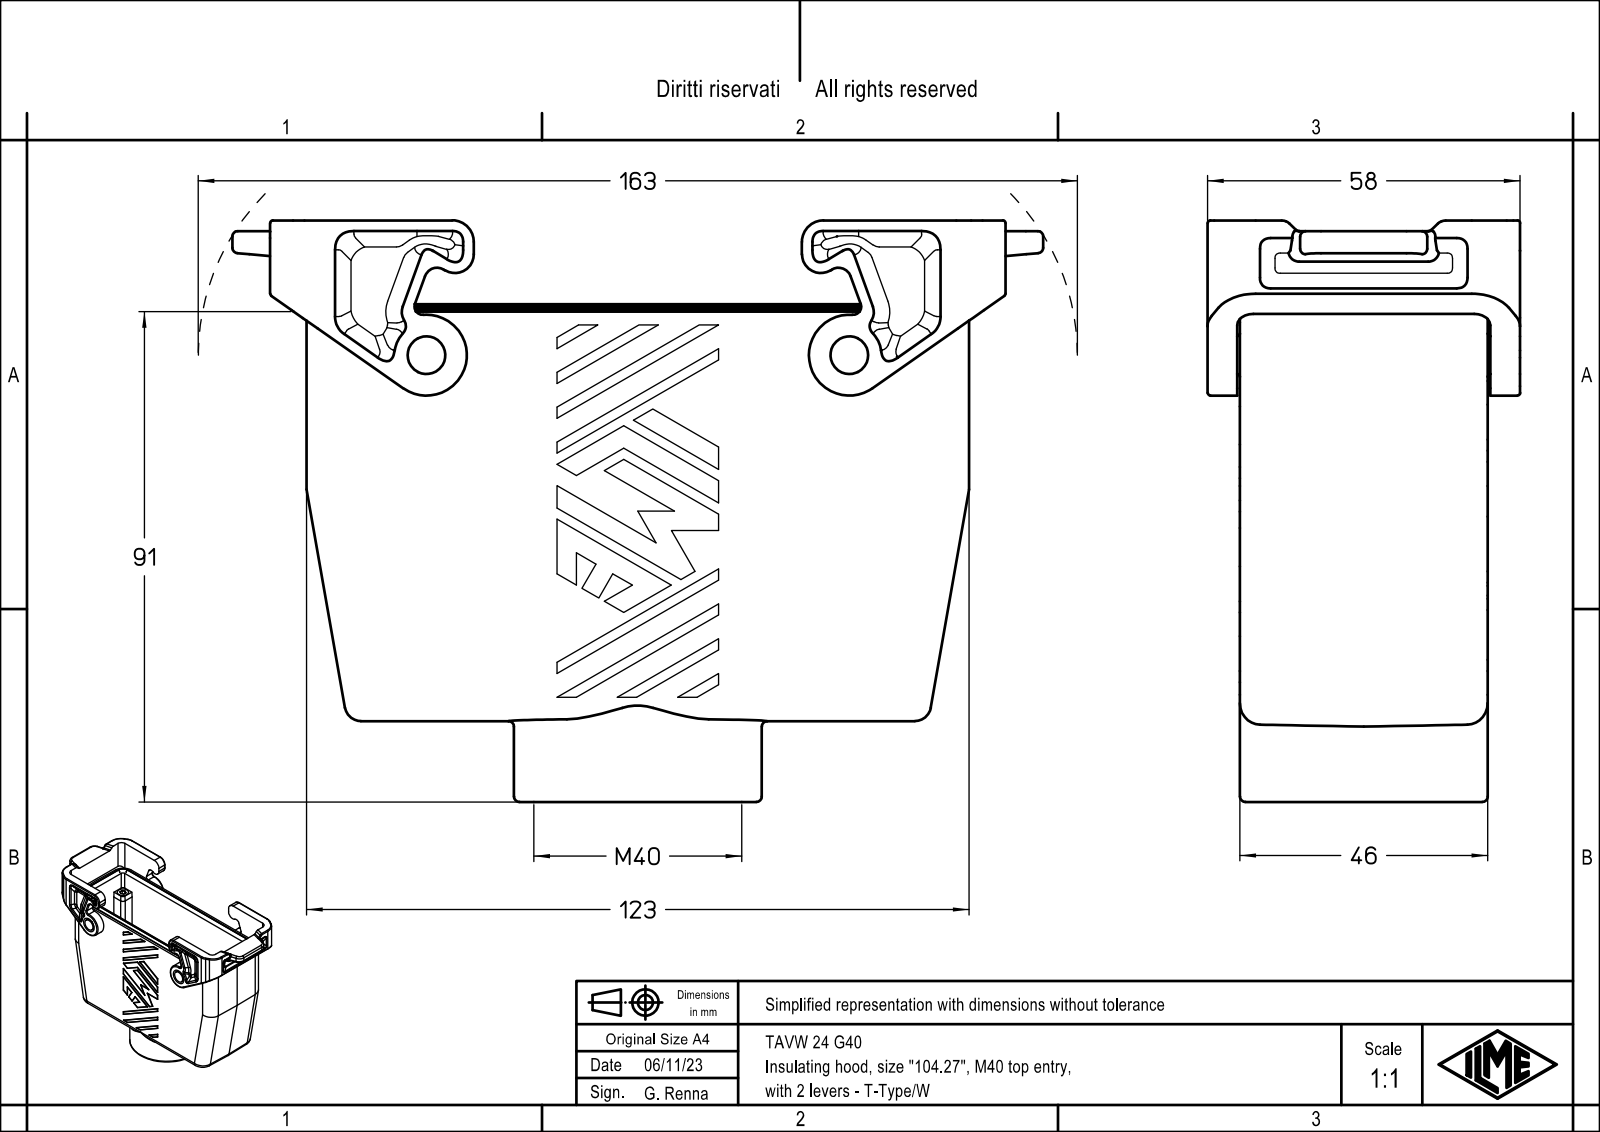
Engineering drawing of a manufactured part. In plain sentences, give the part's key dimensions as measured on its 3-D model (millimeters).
The part is named "TAVW 24 G40". Its 3-D file was written by "Creo Elements/Direct Modeling 20.1B 02-Apr-2019 (C) Parametric Technology GmbH (AUTOMOTIVE_DESIGN)". It is 1 solid with 562 faces: 218 planar, 282 cylindrical and 62 other. Overall it measures 150.5 by 107.9 by 58 millimeters. Its volume is 179 658 cubic millimeters and its surface area 70 873 square millimeters. Round holes: 1 of diameter 34, 1 of diameter 38.6. Round bosses or shafts: 2 of diameter 7, 1 of diameter 46. Partial cylindrical surfaces (rounded edges, fillets, slot ends): 88 of radius 0.15, 20 of radius 3, 16 of radius 1, 16 of radius 2, 10 of radius 1.5, 8 of radius 1.3, 8 of radius 6, 8 of radius 7. The main face-to-face distances are 5.4, 40.6, 35.2, 46, 0.5, 5.9, 41.1, 46.5, 5.5, 52.
